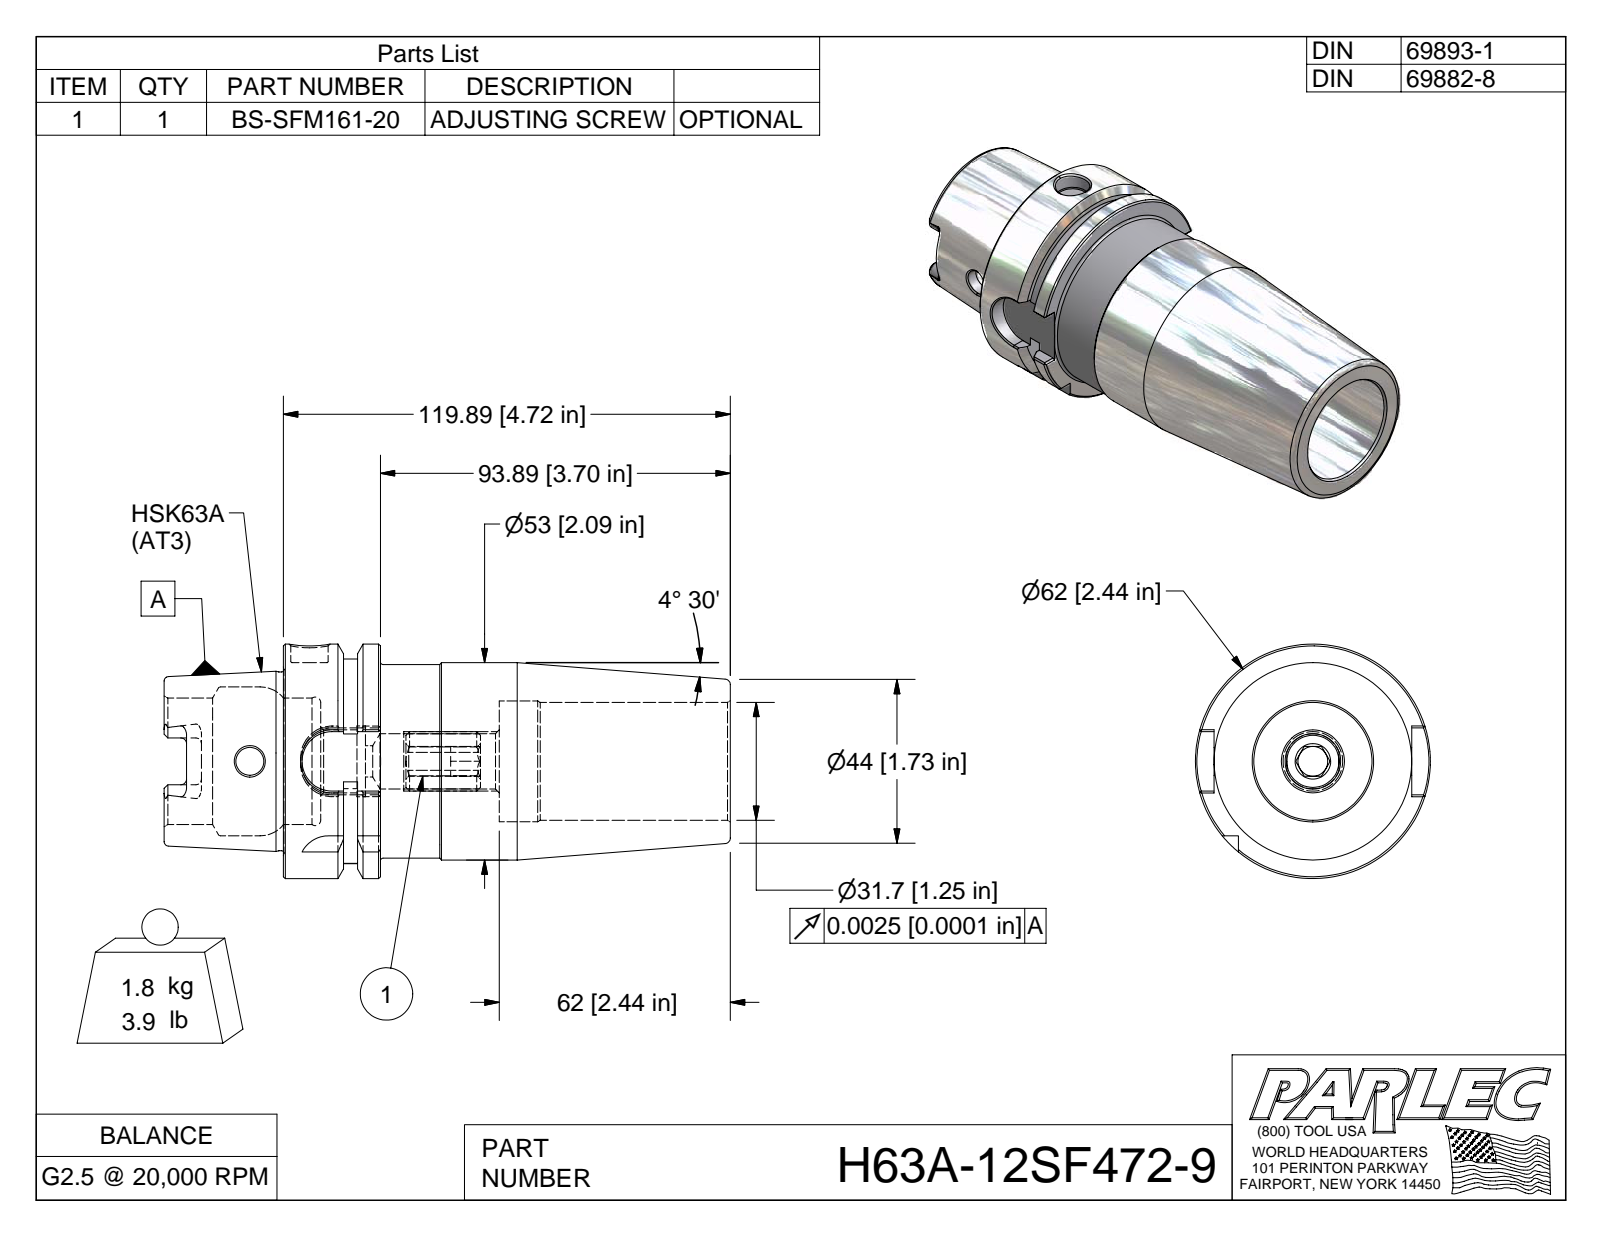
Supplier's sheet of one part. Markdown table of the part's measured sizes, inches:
| quantity | value |
| --- | --- |
| part name | H63A-12SF472-9; H63A-12SF472-9-1; BS-SFM161-20 |
| STEP written by | Autodesk Inventor 2009 (AUTOMOTIVE_DESIGN) |
| units | inches |
| bodies | 2 solids, 167 faces (65 planar, 37 cylindrical, 65 other) |
| overall size | 5.98 × 2.48 × 2.48 |
| volume | 13.07 in³ |
| surface area | 71.29 in² |
| round holes (diameter × count) | 0.295 × 1, 0.394 × 1, 0.666 × 1, 0.749 × 1, 1.248 × 1, 1.278 × 1, 1.339 × 1, 1.575 × 1 |
| round bosses / shafts (diameter × count) | 2.48 × 1, 2.087 × 1, 2.047 × 1, 1.891 × 1 |
| partial cylindrical surfaces (radius × count) | 0.059 × 6, 0.315 × 5, 0.113 × 4, 1.083 × 1 |
| main face-to-face distances | 1.024, 0.241, 0.389, 2.279, 1.256, 0.394, 0.63, 1.885, 4.72, 4.326 |
